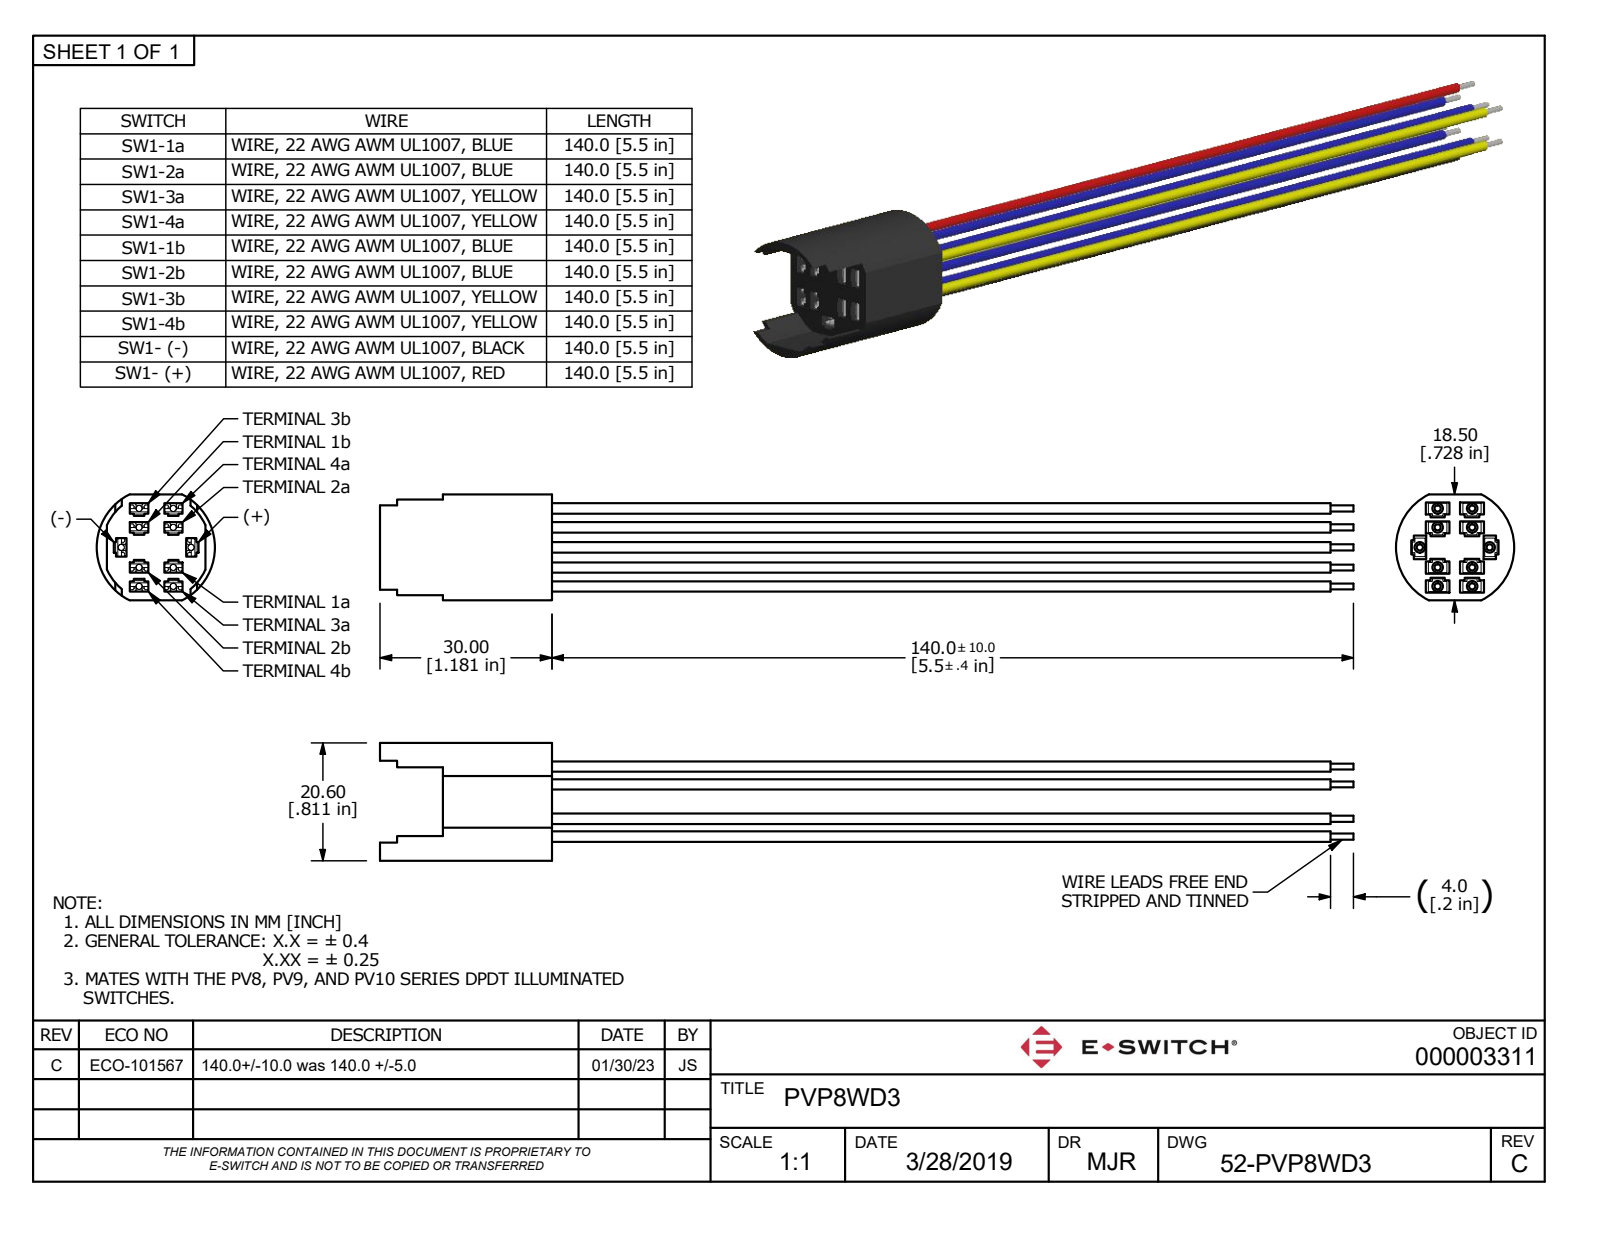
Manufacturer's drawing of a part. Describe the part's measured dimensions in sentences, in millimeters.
The part is named "PVP8WD3". Its 3-D file was written by "Autodesk Inventor 2018 (AP242_MANAGED_MODEL_BASED_3D_ENGINEERING_MIM_LF)". It is 1 solid with 626 faces: 450 planar, 116 cylindrical and 60 other. Overall it measures 170 by 20.6 by 18.5 millimeters. Its volume is 8 957 cubic millimeters and its surface area 13 766 square millimeters. Round bosses or shafts: 10 of diameter 1.8. Partial cylindrical surfaces (rounded edges, fillets, slot ends): 60 of radius 0.25, 20 of radius 0.5, 10 of radius 0.52, 1 of radius 9.45, 1 of radius 10.3. The main face-to-face distances are 3.3, 19, 2.2, 2.37, 13.2, 12.27, 18.5, 10.07, 9.9, 2.6.
